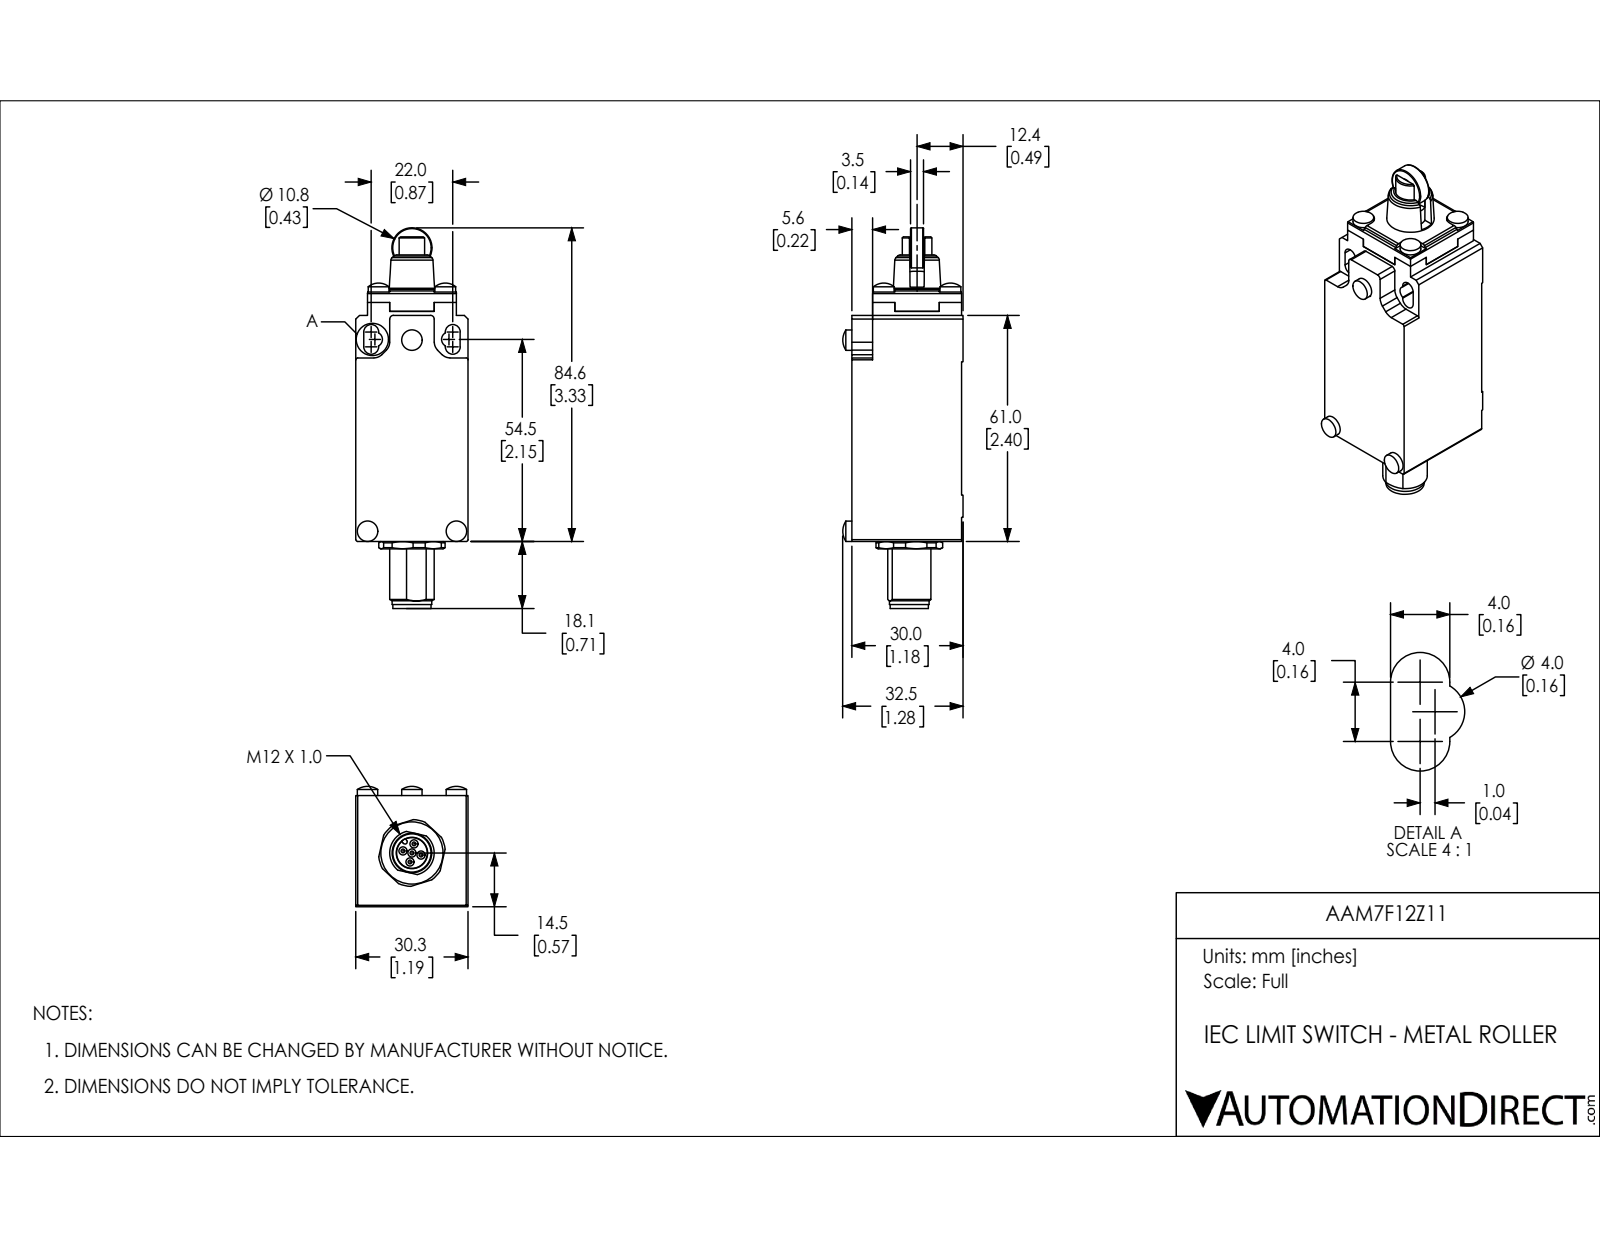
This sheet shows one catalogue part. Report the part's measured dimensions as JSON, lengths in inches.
{"part_name": "AAM7F12Z11", "step_written_by": "SolidWorks 2018 (AUTOMOTIVE_DESIGN)", "units": "inches", "bodies": {"solids": 5, "faces": 317, "planar": 131, "cylindrical": 133, "other": 53}, "overall_size": [4.043, 1.28, 1.193], "volume_in3": 3.665, "surface_area_in2": 25.49, "round_holes": [[0.087, 5], [0.319, 1], [0.512, 1], [0.551, 1], [0.63, 1]], "round_bosses_or_shafts": [[0.22, 5], [0.055, 5], [0.039, 5], [0.217, 3], [0.425, 1], [0.421, 1], [0.406, 1], [0.315, 1]], "partial_cylinders_radius": [[0.039, 10], [0.118, 8], [0.079, 6], [0.02, 4], [0.024, 1], [0.236, 1], [0.354, 1], [0.394, 1]], "face_to_face_distances": [1.193, 1.165, 0.016, 1.181, 2.444, 0.945, 0.236, 2.445, 0.039, 0.15], "hole_center_spacings": [0.098, 0.139, 0.197, 0.026, 0.083, 0.114, 0.142, 0.18]}
